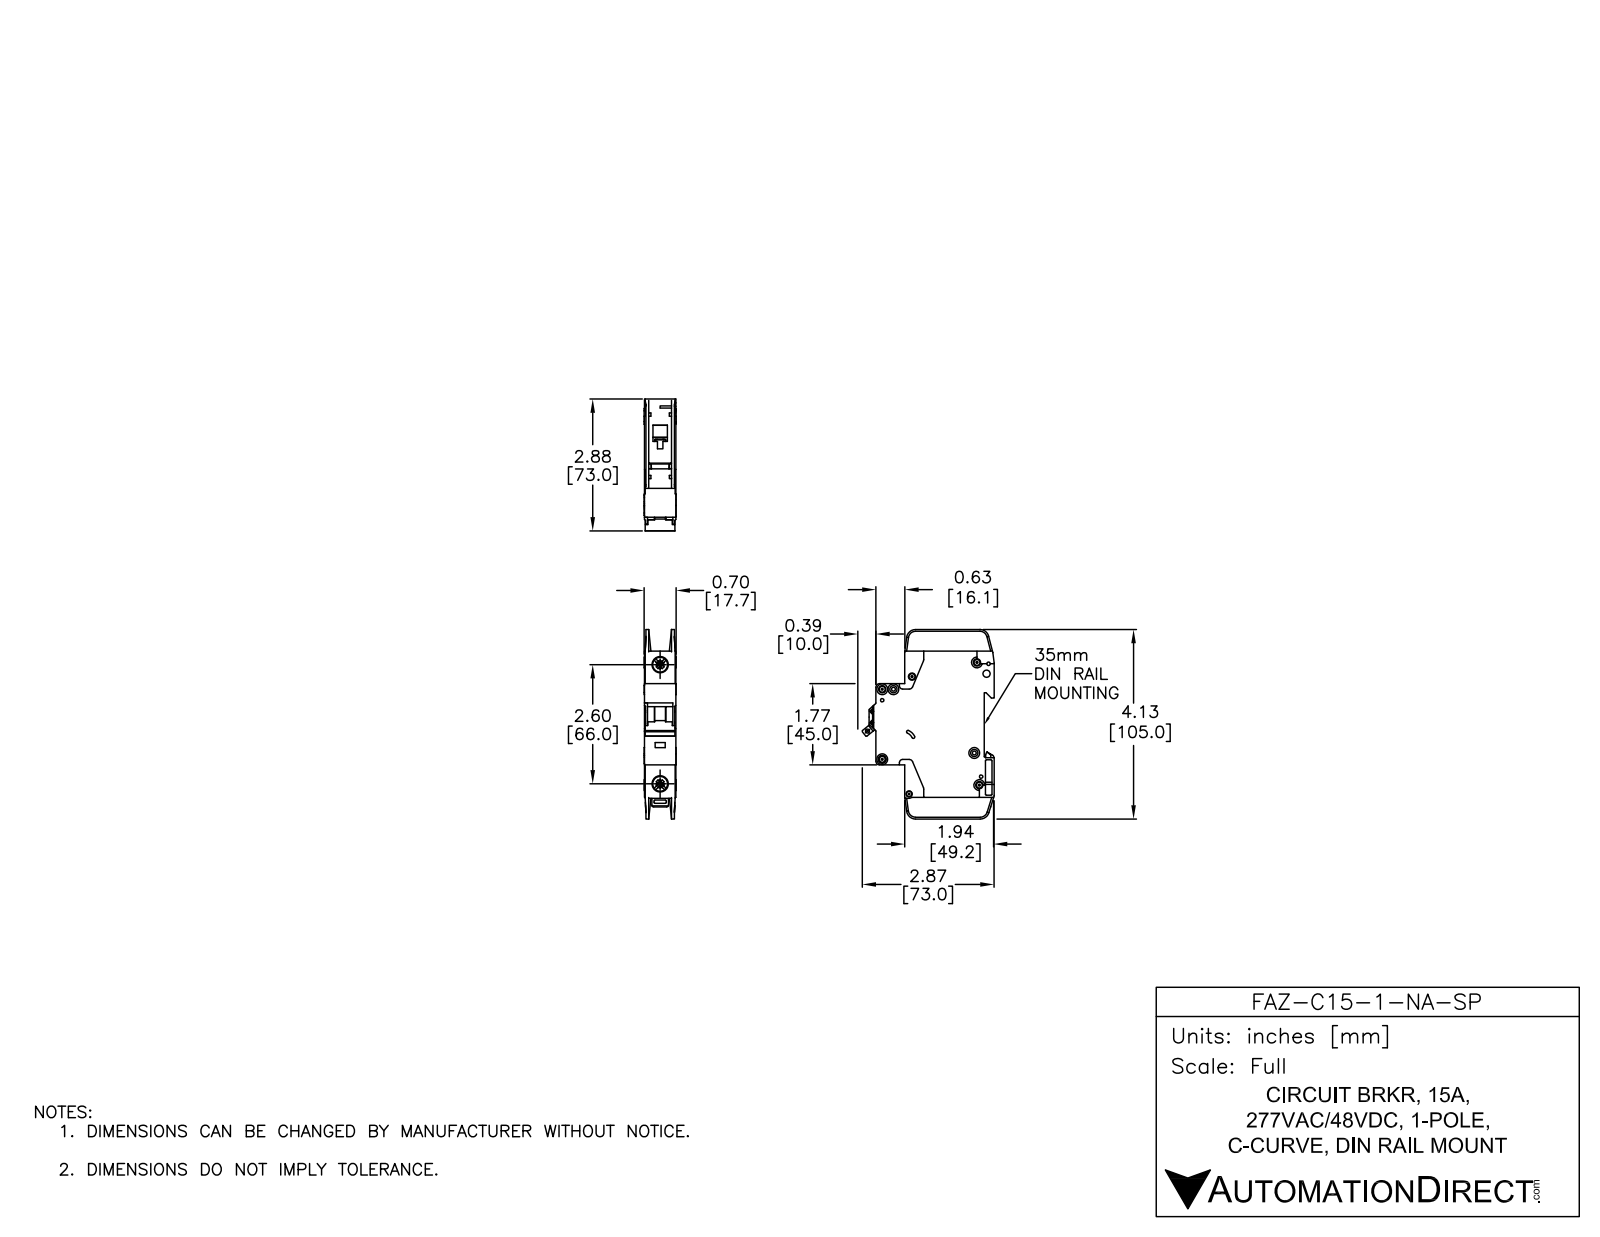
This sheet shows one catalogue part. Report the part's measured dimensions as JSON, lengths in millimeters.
{"part_name": "FAZ-C15-1-NA-SP", "step_written_by": "SolidWorks 2014 (AUTOMOTIVE_DESIGN)", "units": "millimeters", "bodies": {"solids": 3, "faces": 784, "planar": 409, "cylindrical": 263, "other": 112}, "overall_size": [105, 73.04, 17.7], "volume_mm3": 77695, "surface_area_mm2": 24740, "round_holes": [[3.6, 7], [1.09, 2], [1.5, 2], [4, 2], [7.15, 2], [8.2, 2], [1.9, 1], [2.15, 1], [2.2, 1], [2.55, 1], [3.3, 1], [3.4, 1]], "round_bosses_or_shafts": [[6, 7], [2.5, 1]], "partial_cylinders_radius": [[0.25, 29], [0.5, 18], [1, 10], [2, 10], [5, 5], [4, 4], [1.8, 3], [0.2, 2]], "face_to_face_distances": [17.5, 15.05, 0.7, 2.45, 1.75, 15.75, 13.3, 14, 12.6, 2], "hole_center_spacings": [6.2, 5.19, 6.1, 8.19, 8.56, 8.7, 11.11, 12.45]}
